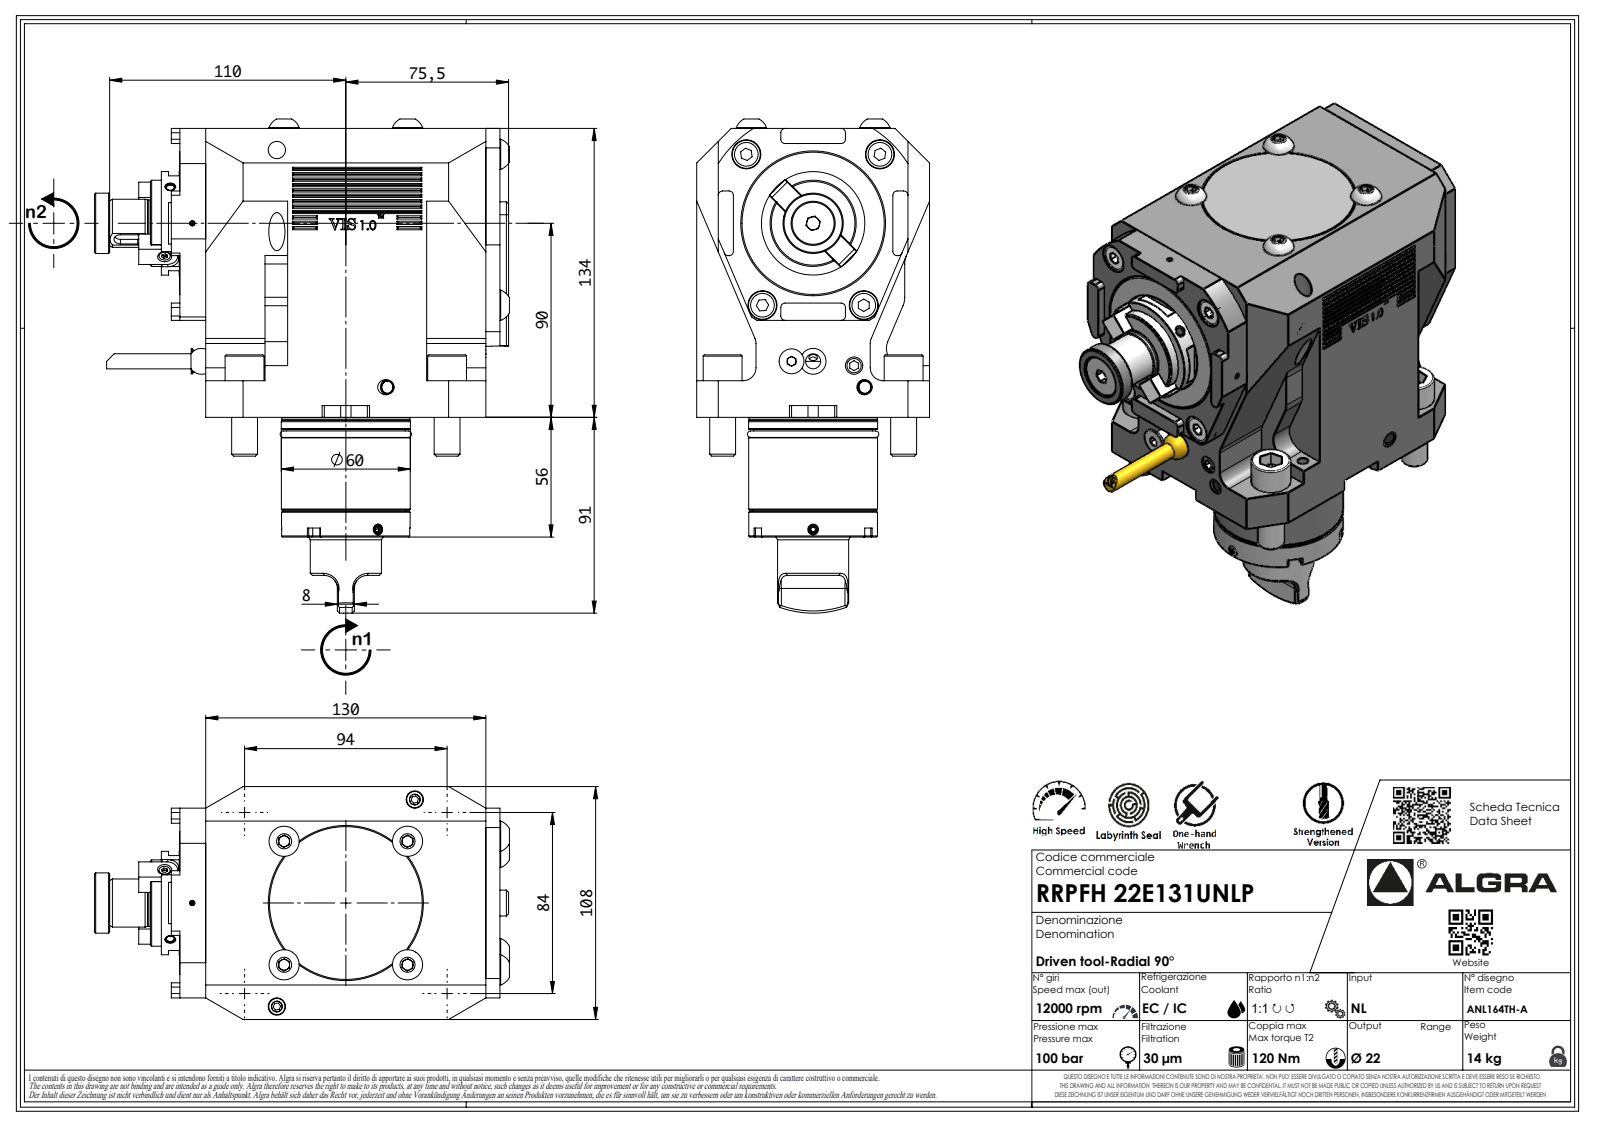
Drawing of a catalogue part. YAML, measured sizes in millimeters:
part_name: "RRPFH22E131UNLP"
step_written_by: "SolidWorks 2023 (AUTOMOTIVE_DESIGN)"
units: millimeters
bodies: {solids: 1, faces: 1011, planar: 694, cylindrical: 134, other: 183}
overall_size: [224.8, 192.1, 108]
volume: 2012000
surface_area: 127259
round_holes:
  - {diameter: 2.1, count: 1}
round_bosses_or_shafts:
  - {diameter: 18, count: 4}
  - {diameter: 12, count: 4}
  - {diameter: 59.9, count: 1}
  - {diameter: 59.8, count: 1}
  - {diameter: 59.7, count: 1}
  - {diameter: 59.5, count: 1}
  - {diameter: 55.2, count: 1}
  - {diameter: 48, count: 1}
partial_cylinders:
  - {radius: 0.2, count: 21}
  - {radius: 8, count: 18}
  - {radius: 2, count: 16}
  - {radius: 6, count: 11}
  - {radius: 0.33, count: 7}
  - {radius: 0.52, count: 7}
  - {radius: 3.7, count: 7}
  - {radius: 10, count: 4}
face_to_face_distances: [108, 134, 27.5, 12, 102.5, 6.5, 136.5, 39.5, 38, 5.5]
